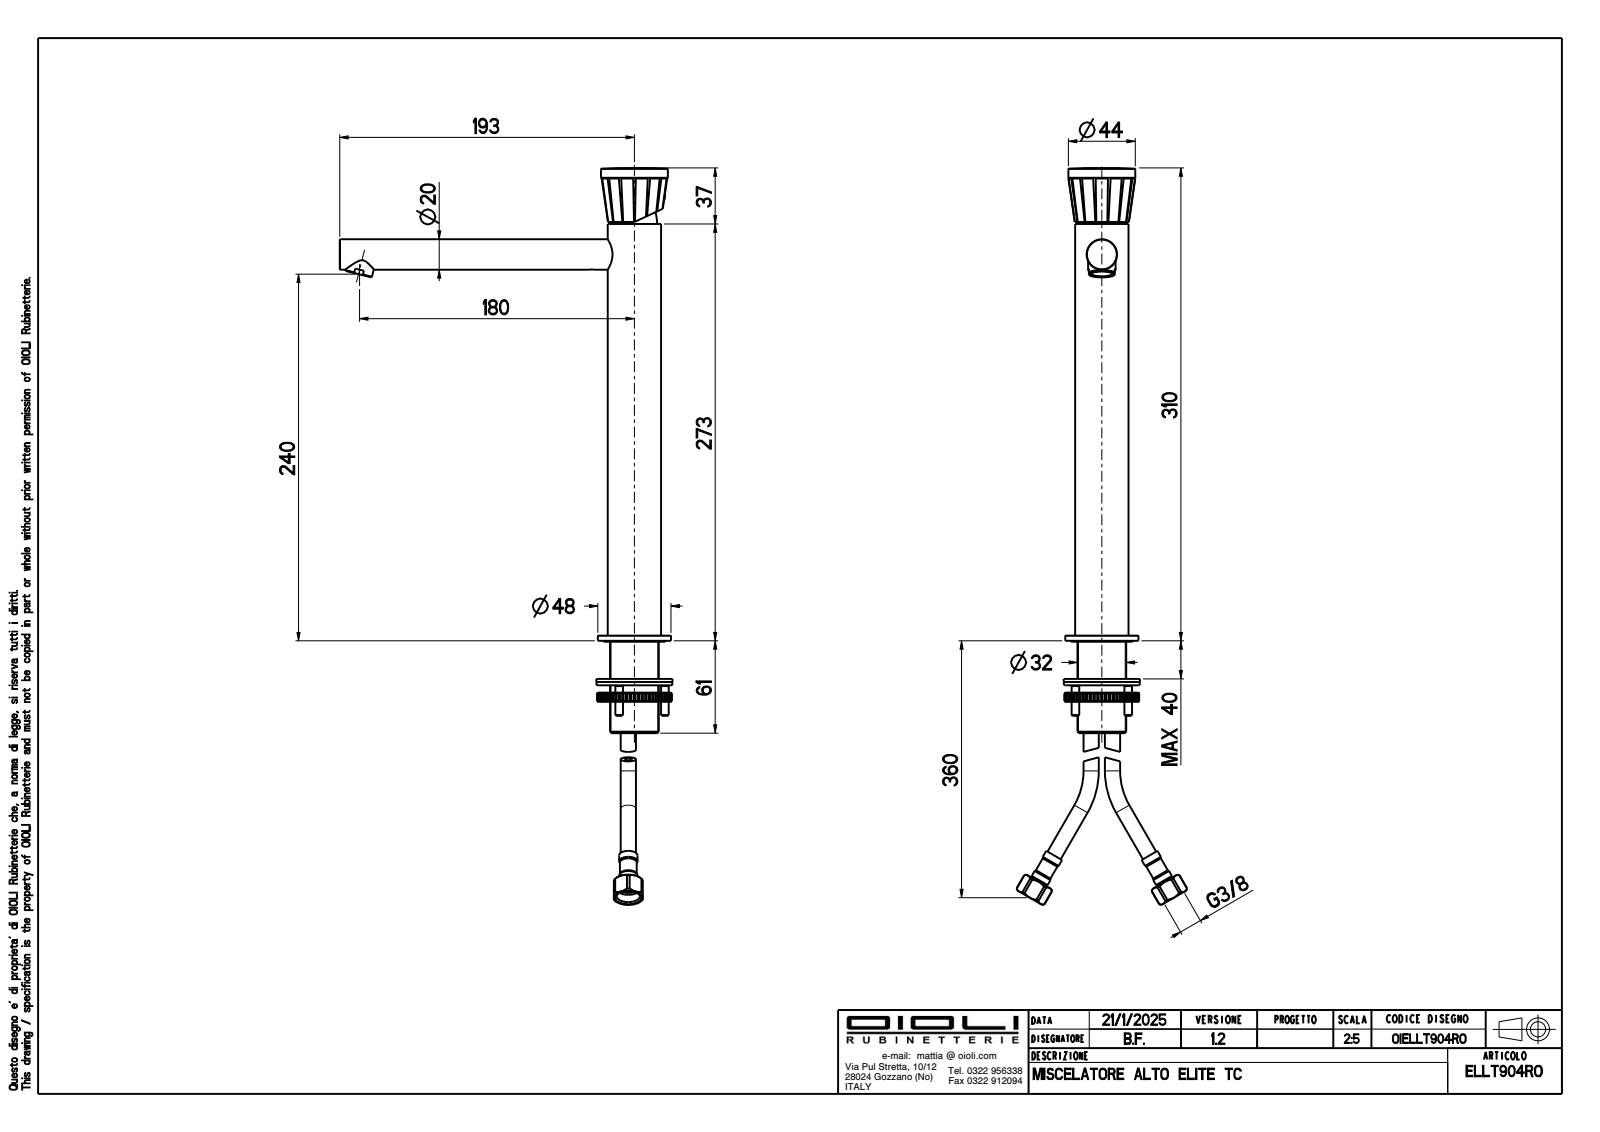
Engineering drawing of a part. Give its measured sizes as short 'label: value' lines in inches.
name: OIBR00604; OIBR00607; OIVT00002; OIAR00063 (+6 more)
written by: CREO PARAMETRIC BY PTC INC, 2024493 (CONFIG_CONTROL_DESIGN)
unit: in
bodies: 9 solids, 371 faces (111 planar, 147 cylindrical, 113 other)
size: 12.212 × 8.557 × 1.89
volume: 12.13 in³; area: 142.1 in²
holes: 4× ⌀0.433, 2× ⌀0.126, 2× ⌀0.197, 2× ⌀0.354, 2× ⌀0.61, 1× ⌀0.13, 1× ⌀0.157, 1× ⌀0.165, 1× ⌀0.209, 1× ⌀0.236, 1× ⌀0.256, 1× ⌀0.374
bosses: 2× ⌀0.65, 2× ⌀0.394, 1× ⌀1.89, 1× ⌀1.728, 1× ⌀1.402, 1× ⌀1.378, 1× ⌀1.26, 1× ⌀1.063
rounds: 10× R0.004, 1× R0.335
face distances: 11.961, 0.134, 12.094, 1.102, 4.858, 4.724, 7.236, 10.764, 10.63, 5.906
hole spacings: 0.317, 0.093, 0.265, 0.352, 0.367, 0.463, 0.609, 0.669
